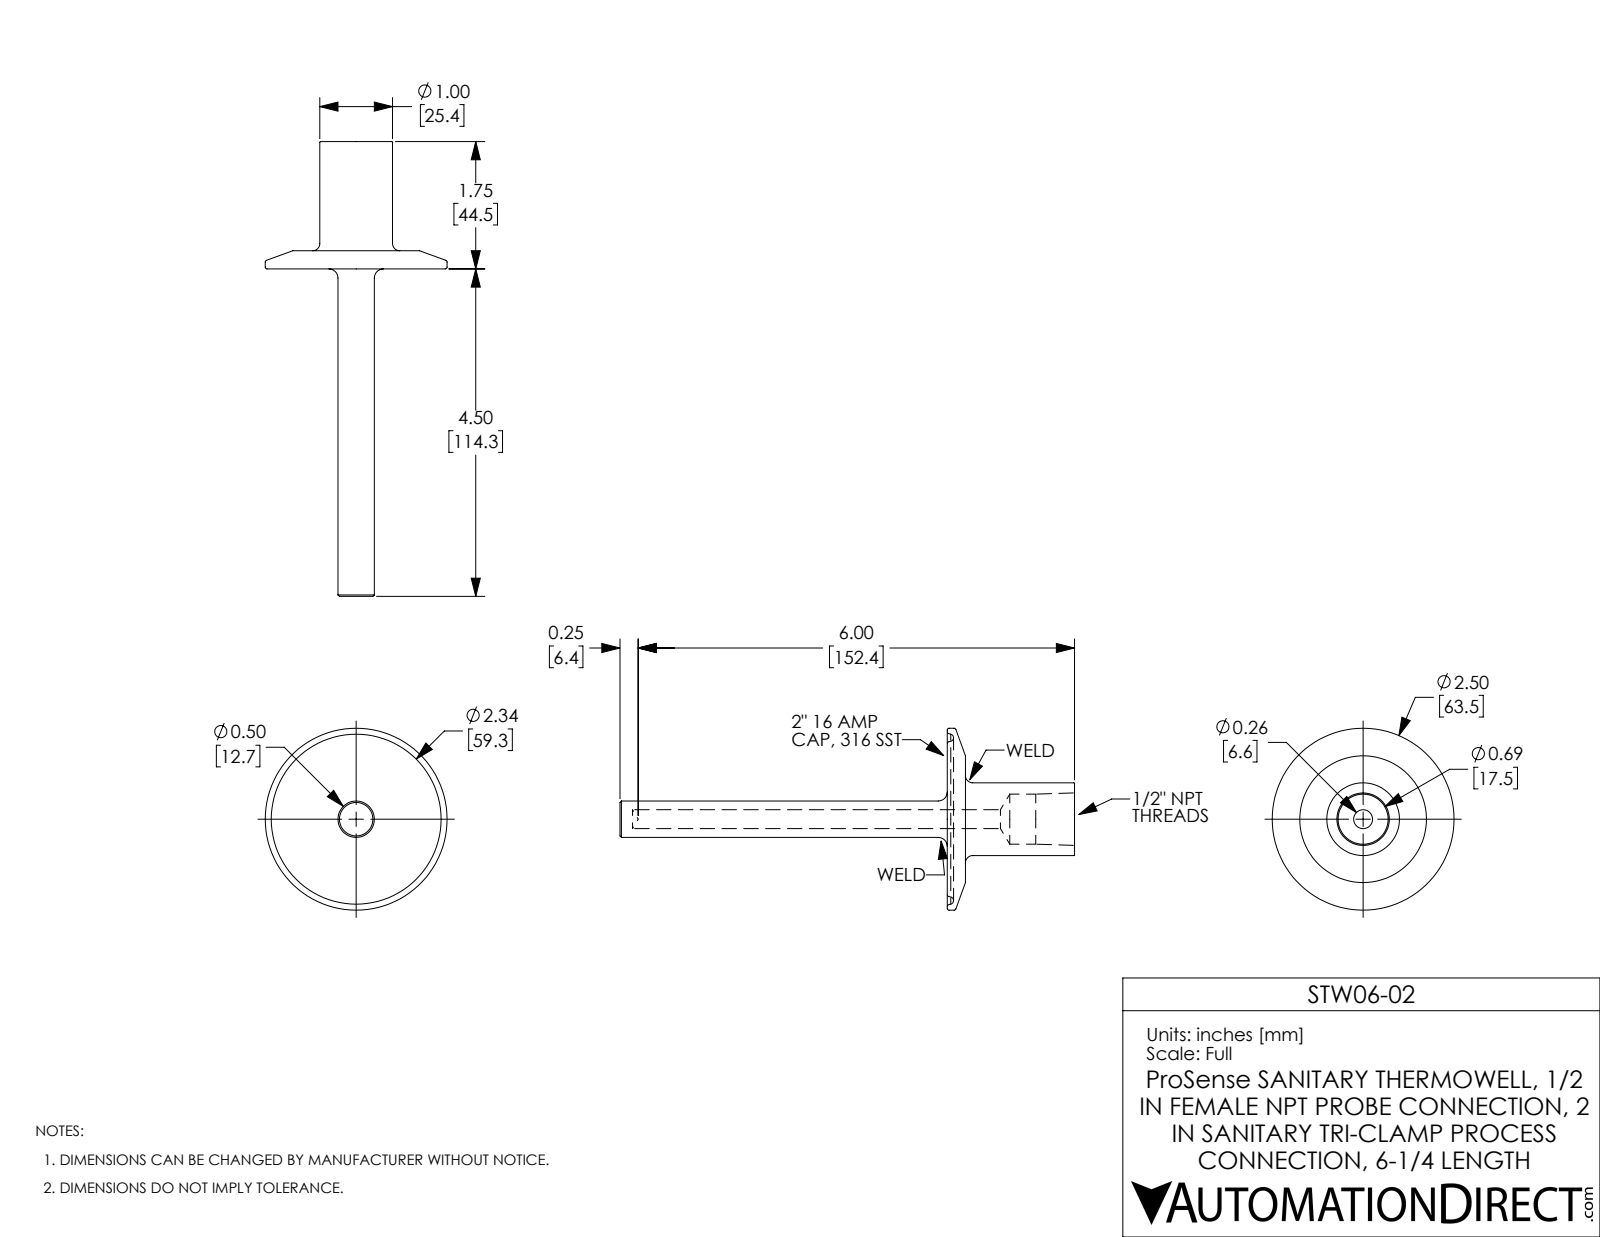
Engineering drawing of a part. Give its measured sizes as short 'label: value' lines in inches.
name: STW06-02
written by: SolidWorks 2017 (AUTOMOTIVE_DESIGN)
unit: in
bodies: 1 solid, 45 faces (5 planar, 10 cylindrical, 30 other)
size: 6.25 × 2.5 × 2.5
volume: 2.426 in³; area: 29.08 in²
holes: 1× ⌀0.26, 1× ⌀0.688
bosses: 1× ⌀2.5, 1× ⌀1, 1× ⌀0.5
face distances: 0.25, 1.5, 1.75, 6.25, 4.75, 4.5
